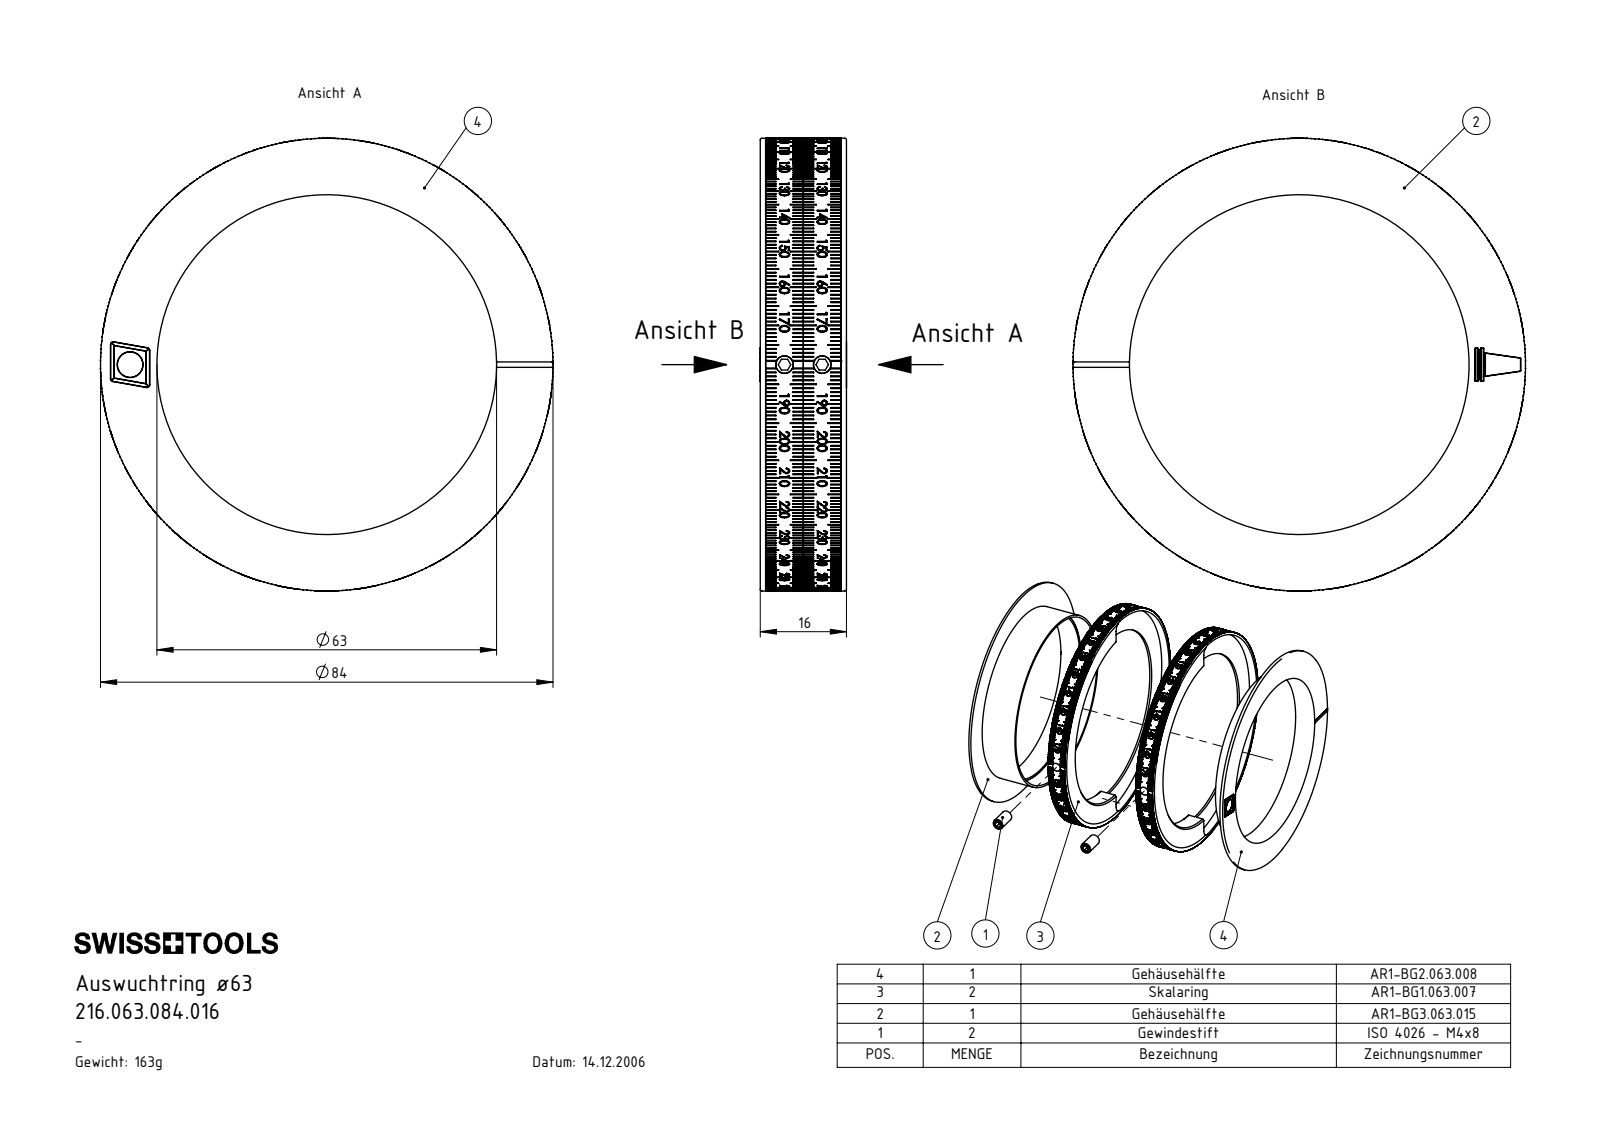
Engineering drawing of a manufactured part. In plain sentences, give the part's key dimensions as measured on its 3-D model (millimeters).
The part is named "AR1-BG3.063.015_A_vereinfachte ansicht; AR1-BG1.063.007_B_vereinfachte ansicht; AR1.U63.001.016; ISO 4026 - M4 x 8 (+1 more)". Its 3-D file was written by "SolidWorks 2017 (AUTOMOTIVE_DESIGN)". It is 6 solids with 86 faces: 45 planar, 27 cylindrical and 14 other. Overall it measures 84 by 84 by 16 millimeters. Its volume is 26 617 cubic millimeters and its surface area 34 769 square millimeters. Round holes: 2 of diameter 3.3, 1 of diameter 63.05, 1 of diameter 64.5, 1 of diameter 66. Round bosses or shafts: 2 of diameter 4, 1 of diameter 84. Partial cylindrical surfaces (rounded edges, fillets, slot ends): 2 of radius 3, 1 of radius 41. The main face-to-face distances are 7, 1, 15, 3.1, 3.9, 6.9, 3, 3.8, 14, 16. The hole center spacings are 7.
